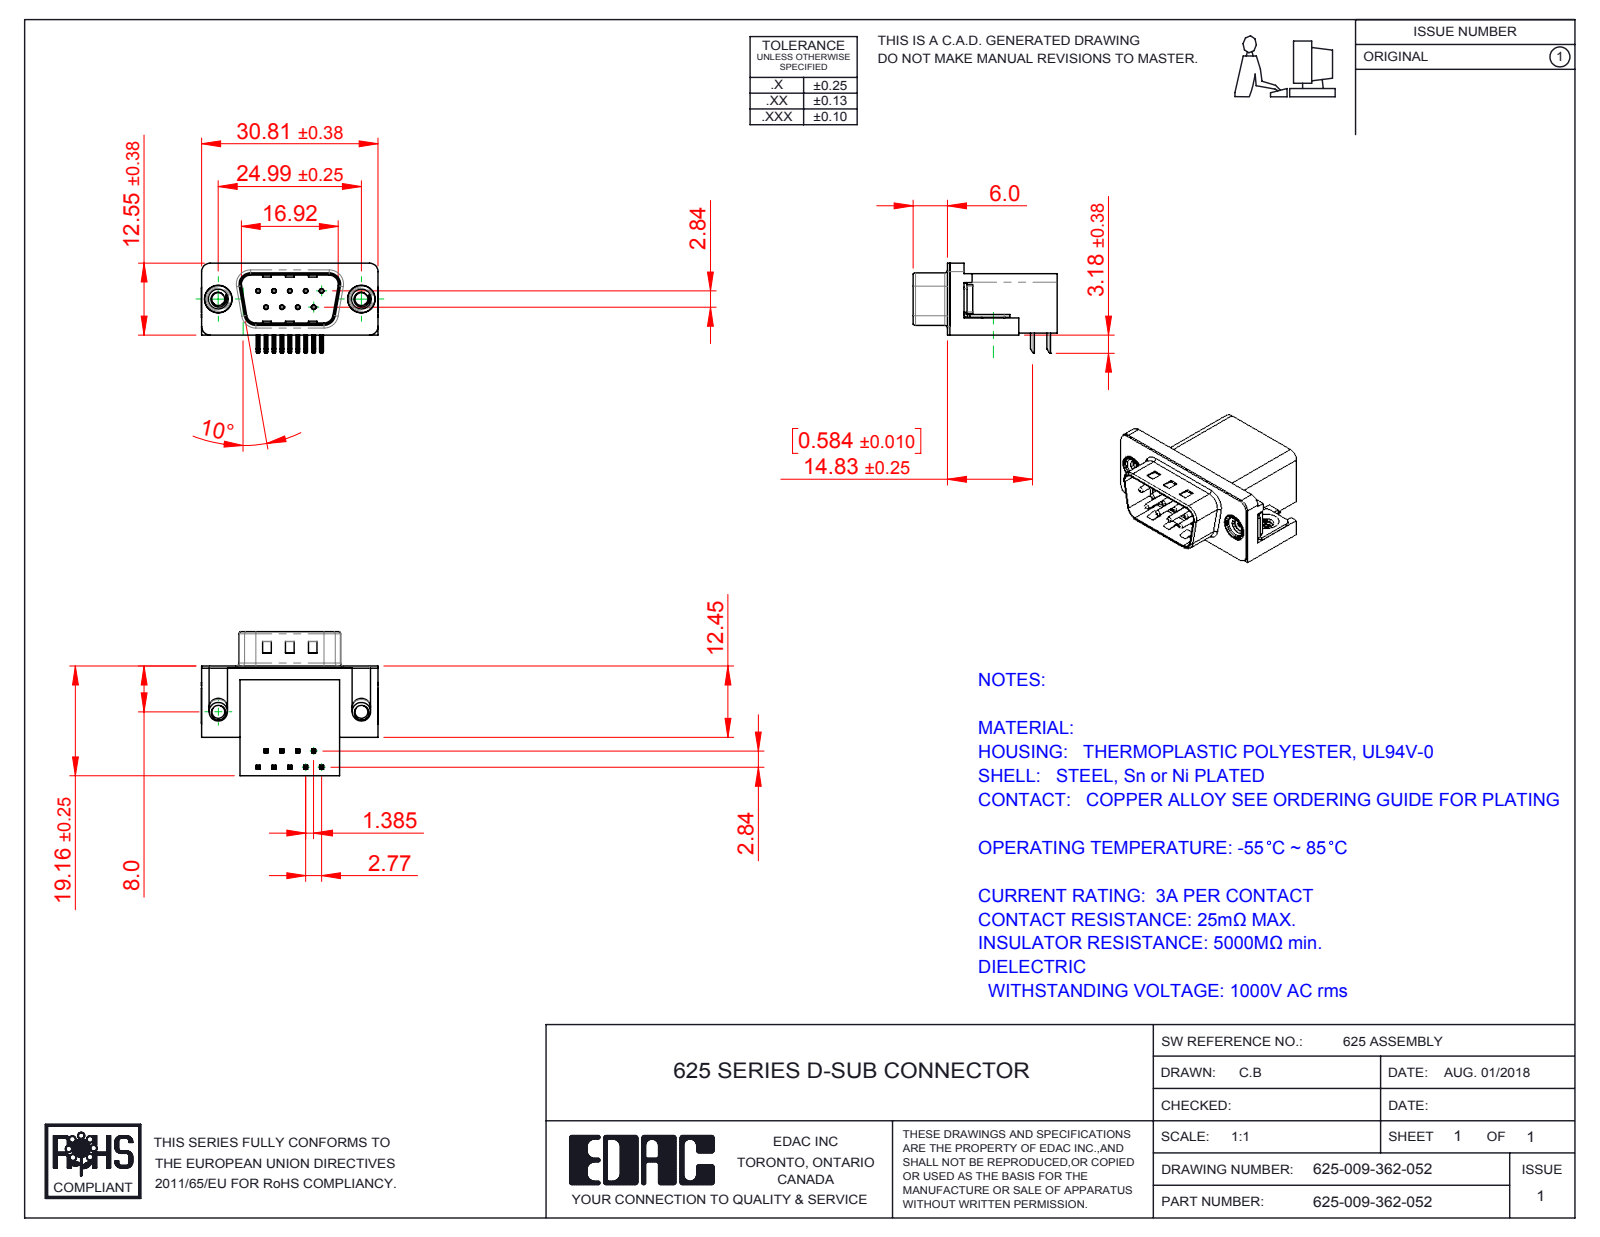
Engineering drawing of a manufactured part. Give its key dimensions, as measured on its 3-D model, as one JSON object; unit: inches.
{"part_name": "625 4-40 Threaded Board Mount; 625 Contact Top; 625 Contact Bottom; 625 4-40 Threaded Rivet (+3 more)", "step_written_by": "SolidWorks 2016 (CONFIG_CONTROL_DESIGN)", "units": "inches", "bodies": {"solids": 15, "faces": 1025, "planar": 575, "cylindrical": 329, "other": 121}, "overall_size": [1.216, 0.991, 0.619], "volume_in3": 0.274, "surface_area_in2": 7.798, "round_holes": [[0.014, 9], [0.031, 9], [0.089, 4], [0.157, 2], [0.189, 2], [0.197, 2]], "round_bosses_or_shafts": [[0.03, 9], [0.193, 2], [0.187, 2], [0.154, 2], [0.128, 2]], "partial_cylinders_radius": [[0.01, 44], [0.005, 18], [0.039, 16], [0.02, 9], [0.059, 8], [0.063, 8], [0.035, 4], [0.079, 4]], "face_to_face_distances": [0.016, 0.407, 0.739, 0.754, 0.114, 0.64, 0.098, 0.014, 0.421, 0.264], "hole_center_spacings": [0.124, 0.109, 0.218, 0.198, 0.198, 0.327, 0.294, 0.295]}
